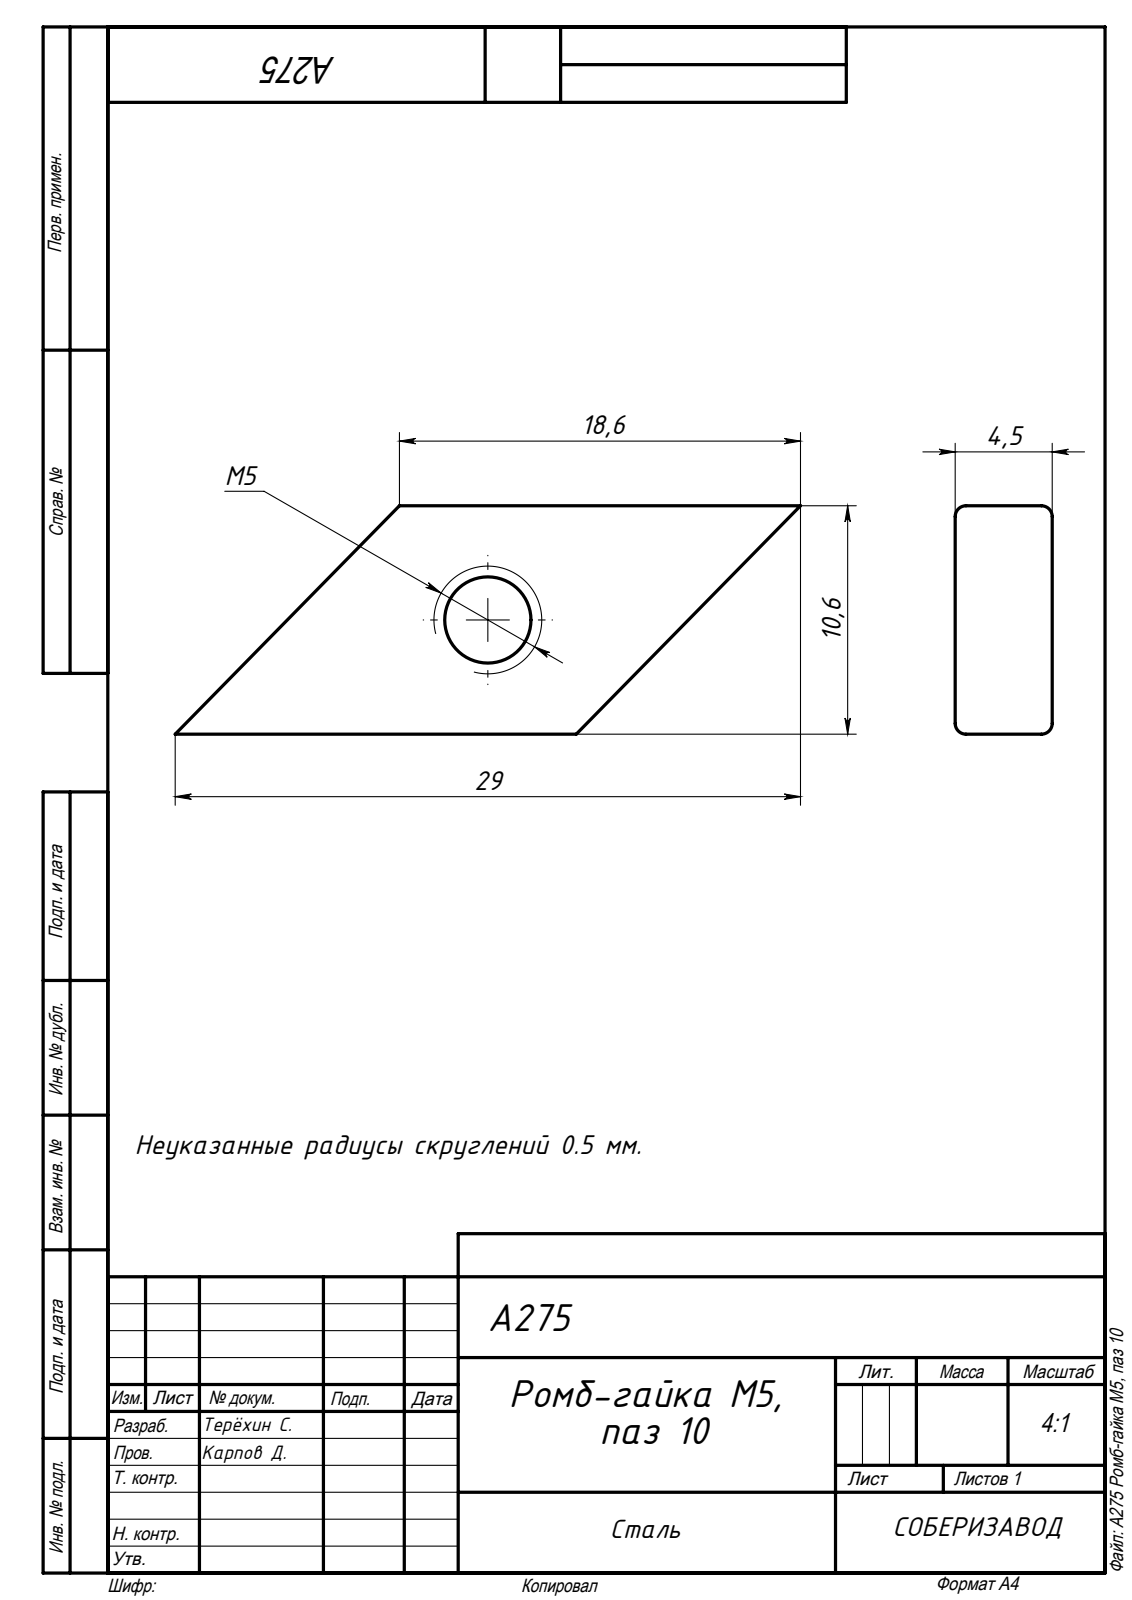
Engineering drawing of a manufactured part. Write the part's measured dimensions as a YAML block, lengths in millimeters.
part_name: "А275 Ромб-гайка М5, паз 10"
step_written_by: "SolidWorks 2020 (AUTOMOTIVE_DESIGN)"
units: millimeters
bodies: {solids: 1, faces: 16, planar: 6, cylindrical: 10, other: 0}
overall_size: [29, 10.6, 4.5]
volume: 824
surface_area: 698
round_holes:
  - {diameter: 4, count: 1}
partial_cylinders:
  - {radius: 0.5, count: 8}
face_to_face_distances: [4.5, 10.6, 13.28]
